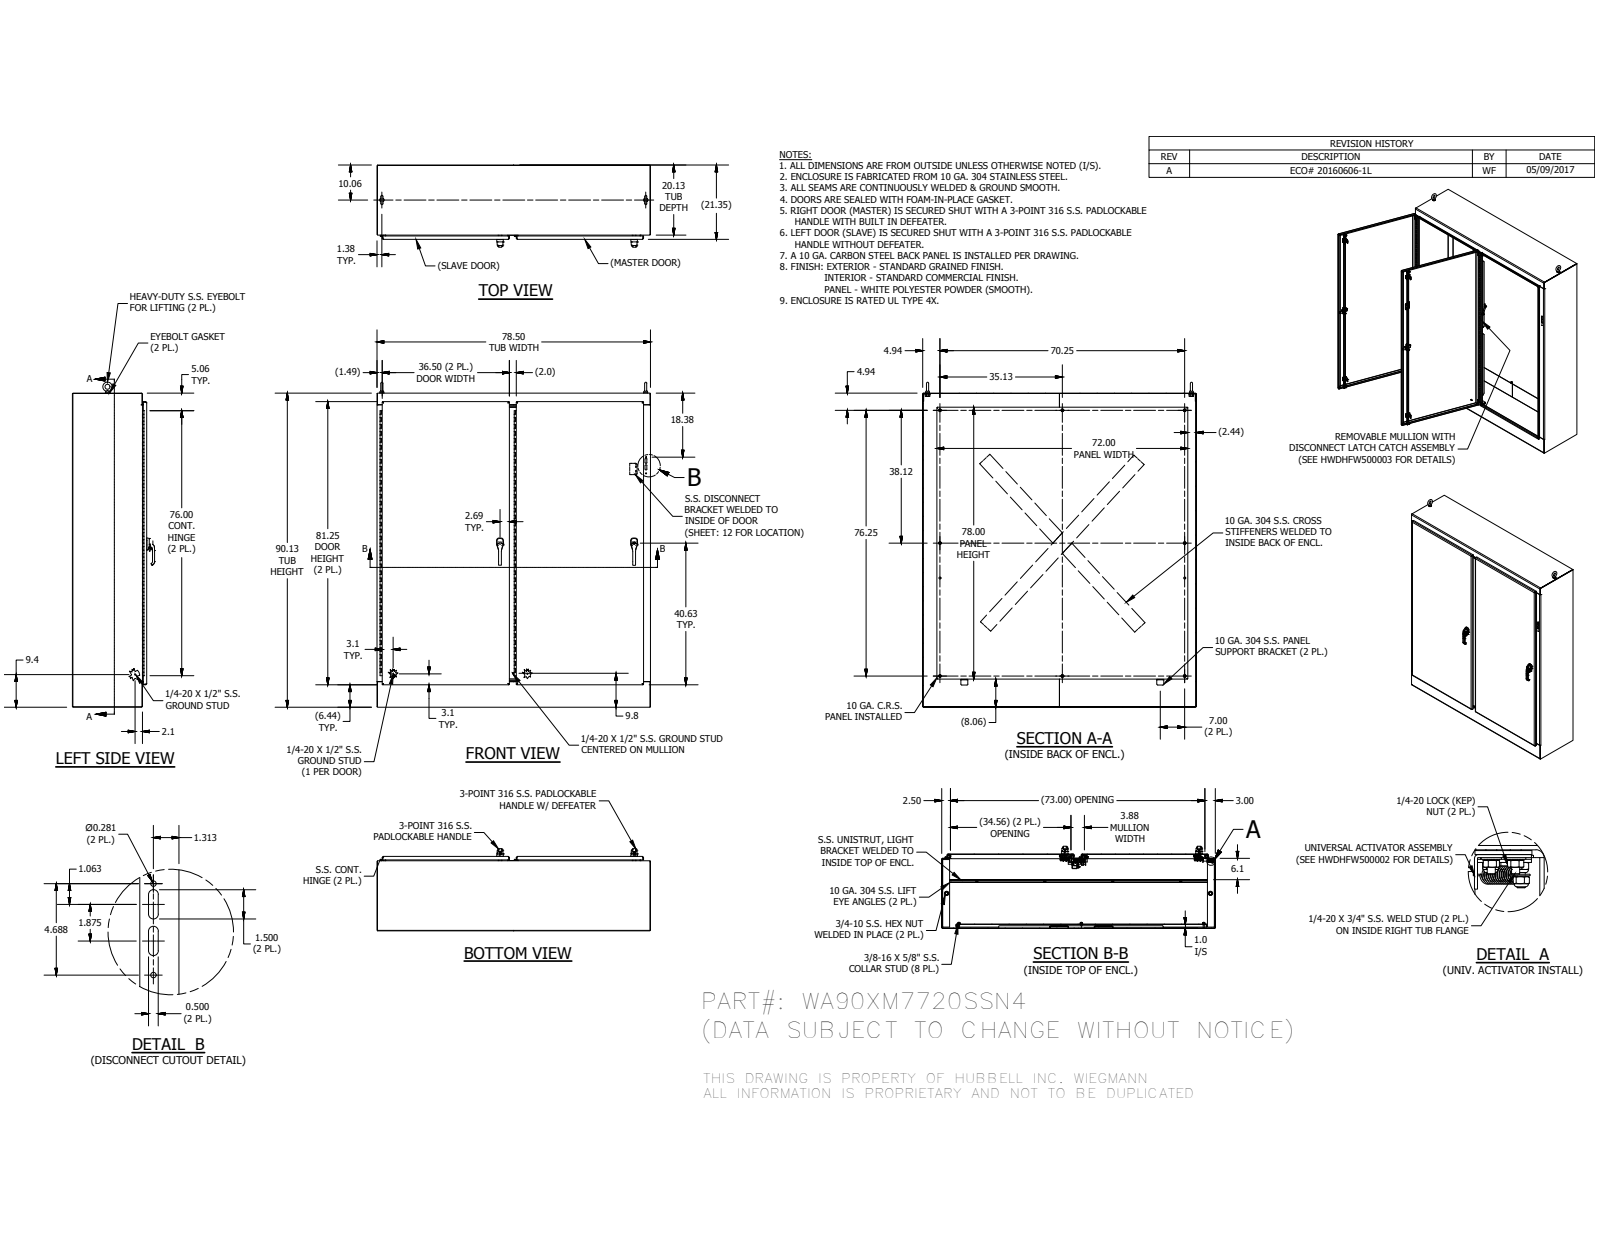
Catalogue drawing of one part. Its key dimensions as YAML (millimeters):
part_name: "WA90XM20SSN4LS; WA90XM77SSN4HFB; WAXM7720SSN4TOP; WAXM7720SSN4BTM (+8 more)"
step_written_by: "Autodesk Inventor 2016 (AUTOMOTIVE_DESIGN)"
units: millimeters
bodies: {solids: 258, faces: 10914, planar: 5214, cylindrical: 3572, other: 2128}
overall_size: [2368.49, 1993.9, 599.42]
volume: 67880000
surface_area: 40010000
round_holes:
  - {diameter: 3.55, count: 48}
  - {diameter: 9.52, count: 18}
  - {diameter: 6.35, count: 16}
  - {diameter: 14.29, count: 10}
  - {diameter: 4.76, count: 9}
  - {diameter: 3.45, count: 8}
  - {diameter: 4.17, count: 8}
  - {diameter: 4.83, count: 8}
  - {diameter: 4.98, count: 8}
  - {diameter: 5.1, count: 8}
  - {diameter: 6.65, count: 8}
  - {diameter: 7.33, count: 8}
round_bosses_or_shafts:
  - {diameter: 8.38, count: 18}
  - {diameter: 6.35, count: 18}
  - {diameter: 15.88, count: 13}
  - {diameter: 8.56, count: 12}
  - {diameter: 9.52, count: 11}
  - {diameter: 14.29, count: 9}
  - {diameter: 7.11, count: 8}
  - {diameter: 6.02, count: 8}
partial_cylinders:
  - {radius: 0.5, count: 358}
  - {radius: 0.3, count: 222}
  - {radius: 0.51, count: 192}
  - {radius: 3.17, count: 47}
  - {radius: 0.47, count: 42}
  - {radius: 1.59, count: 36}
  - {radius: 6.35, count: 31}
  - {radius: 1.27, count: 28}
face_to_face_distances: [3.4, 538.9, 3.41, 535.5, 25.4, 542.3, 28.8, 513.5, 32.21, 28.81]
hole_center_spacings: [973.57, 0.45, 973.5, 973.64, 973.35, 973.79, 1829.12, 0.59]
